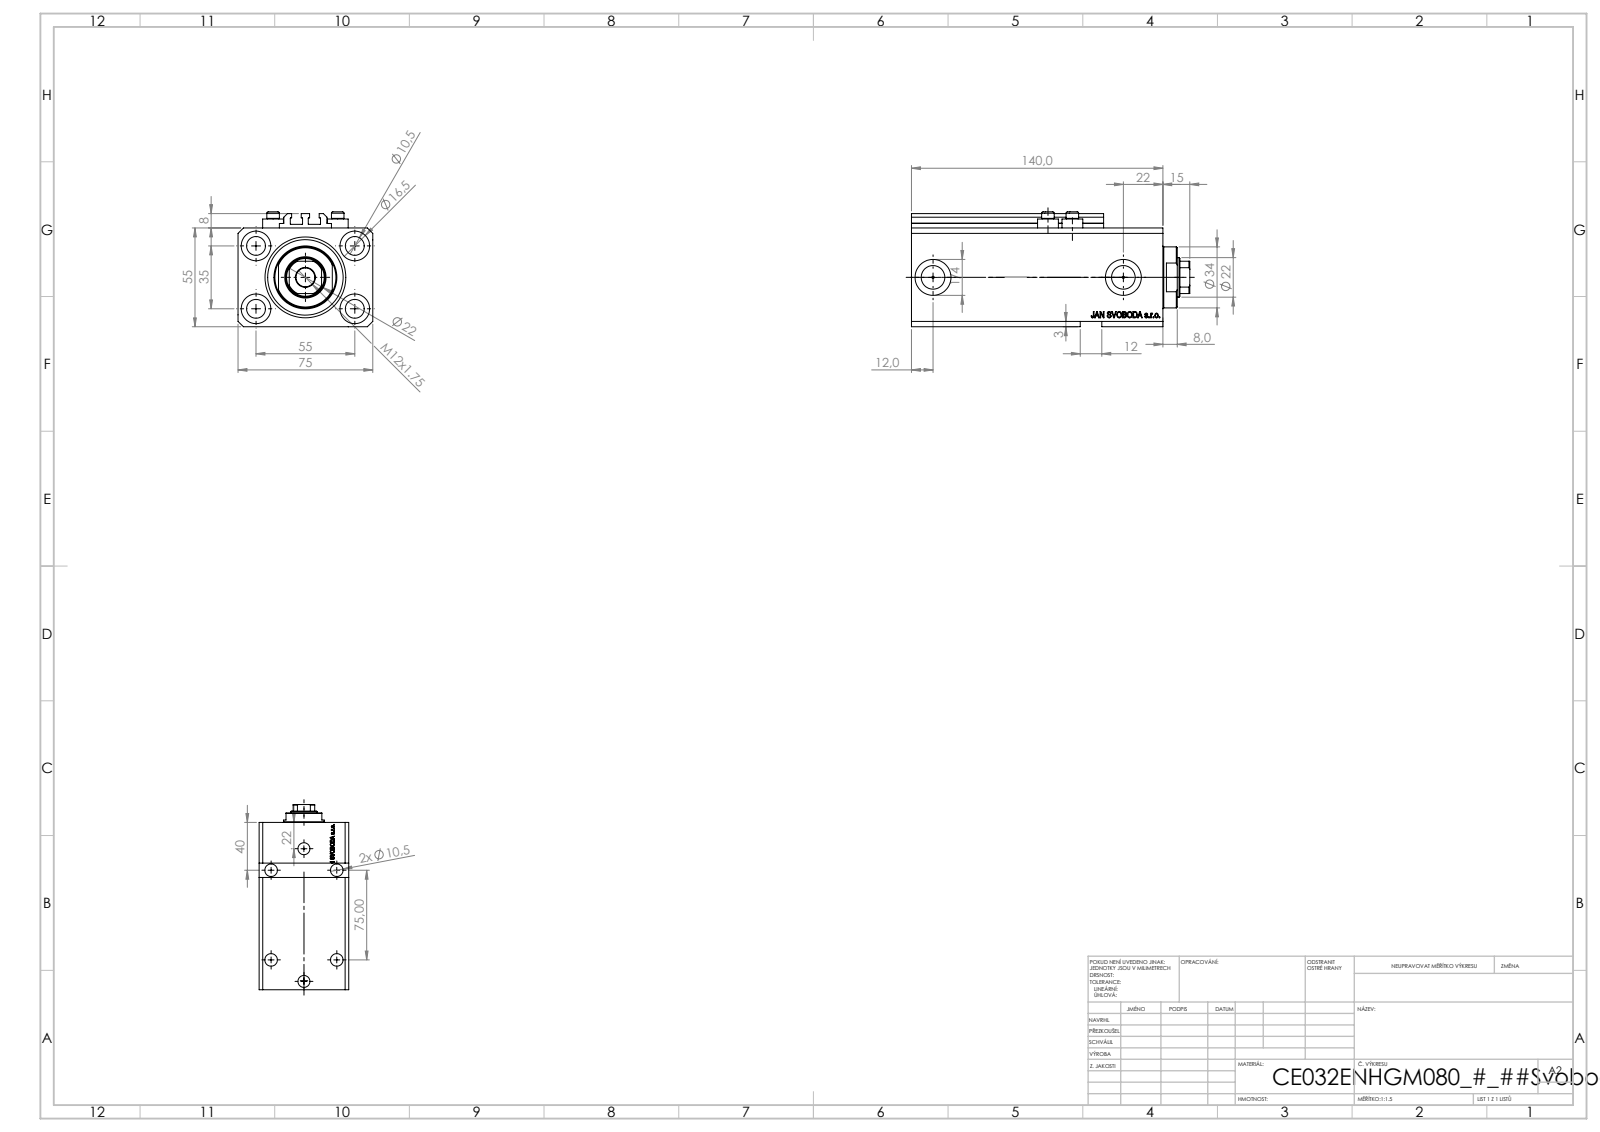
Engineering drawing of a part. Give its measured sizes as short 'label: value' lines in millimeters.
name: V250CE_VC_E; ALLEN BOLT V250CE; V250CE_C_VCP; V250CE_E_Body
written by: SolidWorks 2019 (CONFIG_CONTROL_DESIGN)
unit: mm
bodies: 8 solids, 1084 faces (514 planar, 146 cylindrical, 424 other)
size: 155 × 75 × 64
volume: 485 219 mm³; area: 115 303 mm²
holes: 9× ⌀10.5, 4× ⌀1.25, 4× ⌀4, 4× ⌀16.5, 2× ⌀10, 2× ⌀13.16, 2× ⌀20, 1× ⌀22, 1× ⌀32, 1× ⌀45
bosses: 4× ⌀11.6, 4× ⌀7, 1× ⌀34
rounds: 10× R0.2, 1× R10.5
face distances: 55, 75, 15, 140, 125, 3, 9.9, 57, 115.1, 130.1
hole spacings: 32.6, 32.87, 55, 96.98, 13.6, 14.09, 25.81, 32.58
